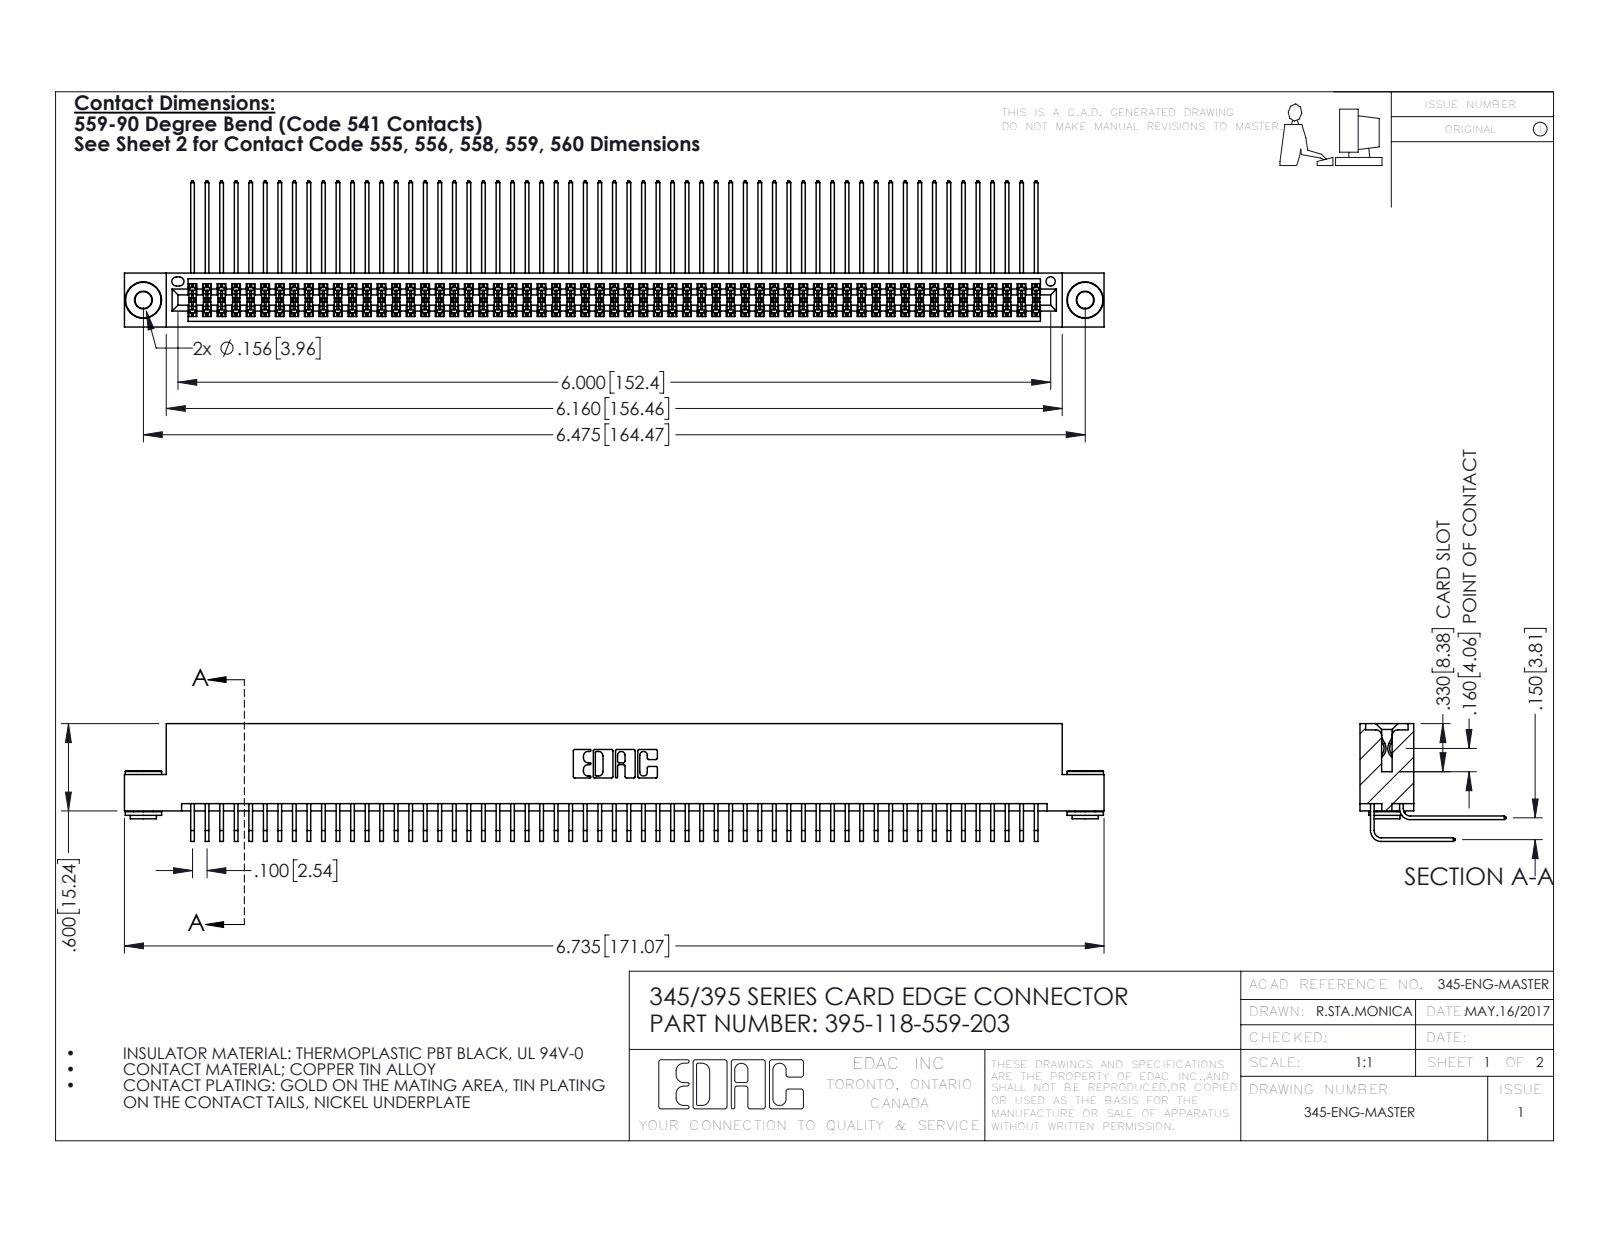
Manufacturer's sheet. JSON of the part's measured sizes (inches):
{"part_name": "345-250-002_345-250-002-102; 345-292-001_559 Tail - 2; 345-292-001_558 559 Tail - 1; 395-118-559-203 (+1 more)", "step_written_by": "SolidWorks 2016 (CONFIG_CONTROL_DESIGN)", "units": "inches", "bodies": {"solids": 121, "faces": 6300, "planar": 4220, "cylindrical": 2072, "other": 8}, "overall_size": [6.735, 1.005, 0.809], "volume_in3": 1.066, "surface_area_in2": 45.83, "round_holes": [[0.116, 2], [0.156, 2], [0.064, 1]], "round_bosses_or_shafts": [[0.25, 2], [0.18, 2], [0.136, 2]], "partial_cylinders_radius": [[0.006, 177], [0.01, 22], [0.007, 6], [0.031, 6], [0.026, 3], [0.014, 2], [0.019, 2], [0.022, 2]], "face_to_face_distances": [0.072, 0.298, 0.2, 0.37, 0.025, 0.098, 0.272, 0.225, 0.175, 0.15], "hole_center_spacings": [0.27, 6.239, 6.475]}
